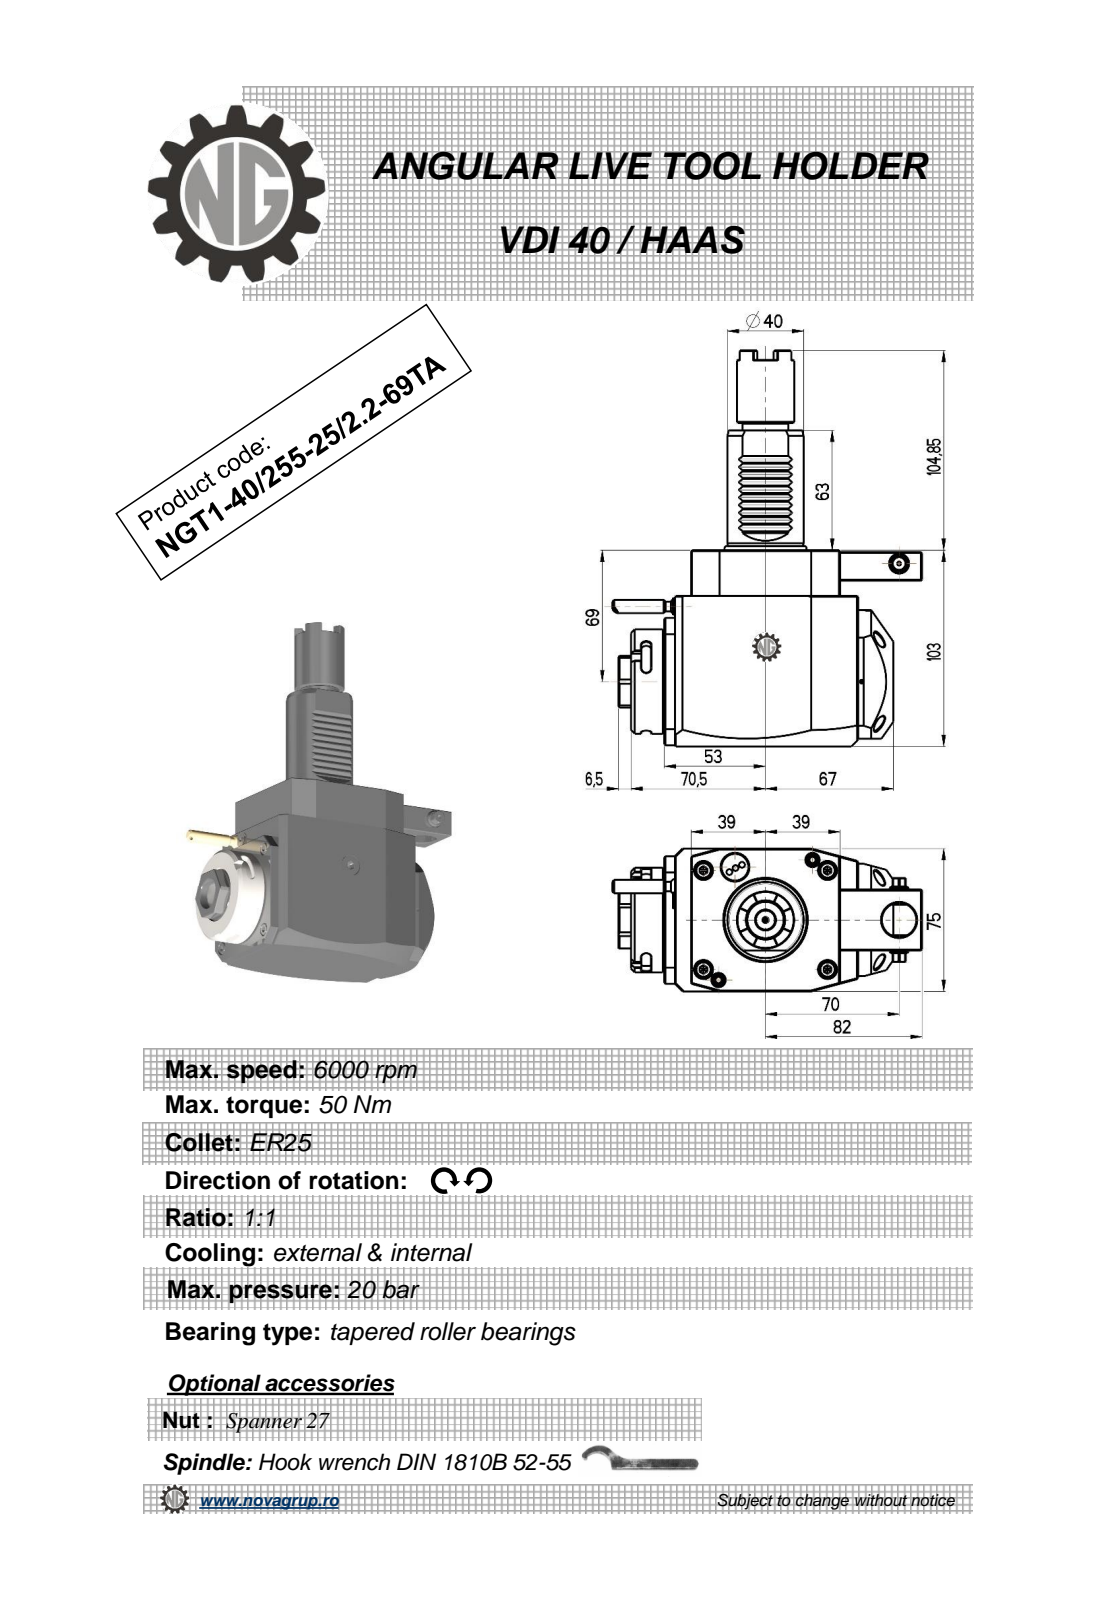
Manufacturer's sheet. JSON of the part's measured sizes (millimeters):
{"part_name": "NGT1_40_255_25_1_2_69TA", "step_written_by": "PRO/ENGINEER BY PARAMETRIC TECHNOLOGY CORPORATION, 2010280 (CONFIG_CONTROL_DESIGN)", "units": "millimeters", "bodies": {"solids": 1, "faces": 393, "planar": 213, "cylindrical": 92, "other": 88}, "overall_size": [207.85, 162.33, 75], "volume_mm3": 926502, "surface_area_mm2": 73448, "round_holes": [[18, 2], [2, 1], [2.5, 1], [3, 1], [9.5, 1], [20, 1]], "round_bosses_or_shafts": [[8.96, 2], [55, 1], [48, 1], [40, 1], [30, 1], [24, 1], [10, 1], [7, 1]], "partial_cylinders_radius": [[0.3, 10], [2.5, 6], [180, 2], [0.5, 1], [3.85, 1], [4.25, 1], [15, 1], [24.5, 1]], "face_to_face_distances": [75, 103, 17.5, 23, 79, 102, 24, 31.5, 14, 87], "hole_center_spacings": [28.11, 43.2, 61.5, 70]}
